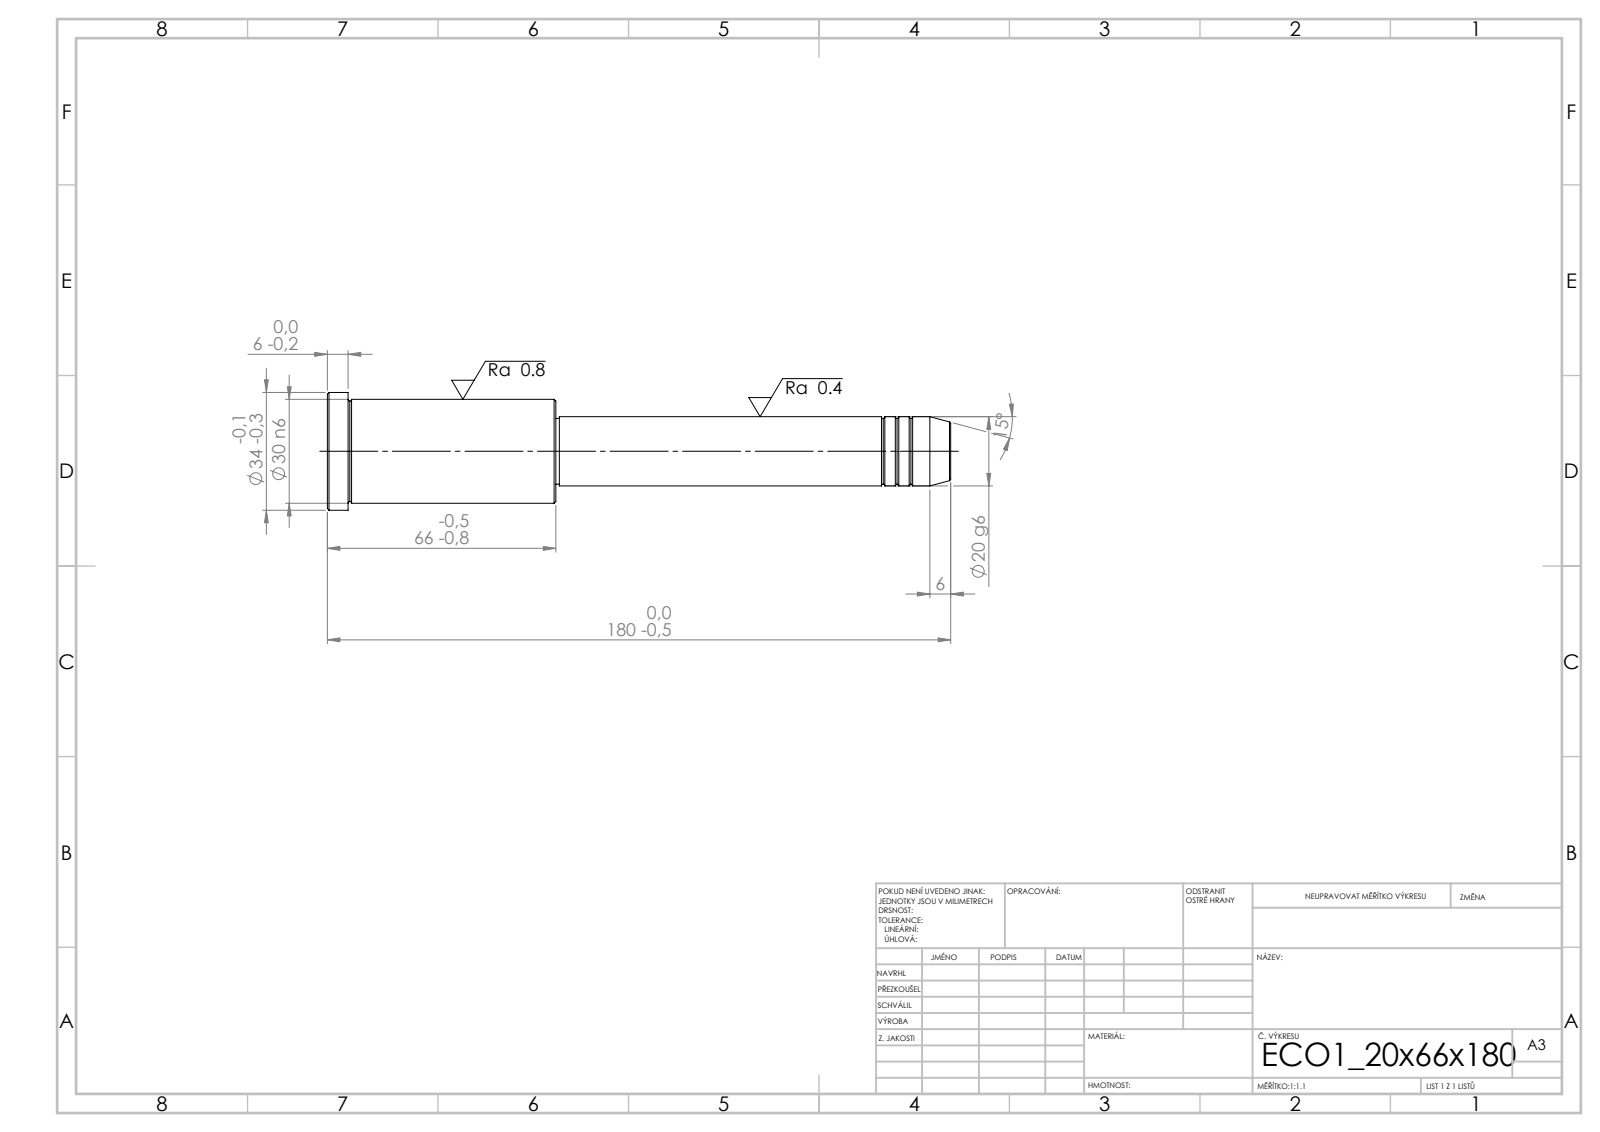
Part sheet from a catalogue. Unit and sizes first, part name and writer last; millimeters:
Units: millimetres
Overall size (bounding box): 180 × 34 × 34
Round bosses / shafts (diameter × count): ⌀34 ×1, ⌀30 ×1, ⌀20 ×1, ⌀19 ×1
Main face-to-face distances: 66, 114, 180, 174, 60, 6, 113, 1, 61, 67
Volume: 83 220 mm³ · Surface area: 15 305 mm²
Bodies: 1 solid, 43 faces (5 planar, 14 cylindrical, 24 other)
STEP written by: SolidWorks 2019 (CONFIG_CONTROL_DESIGN)
